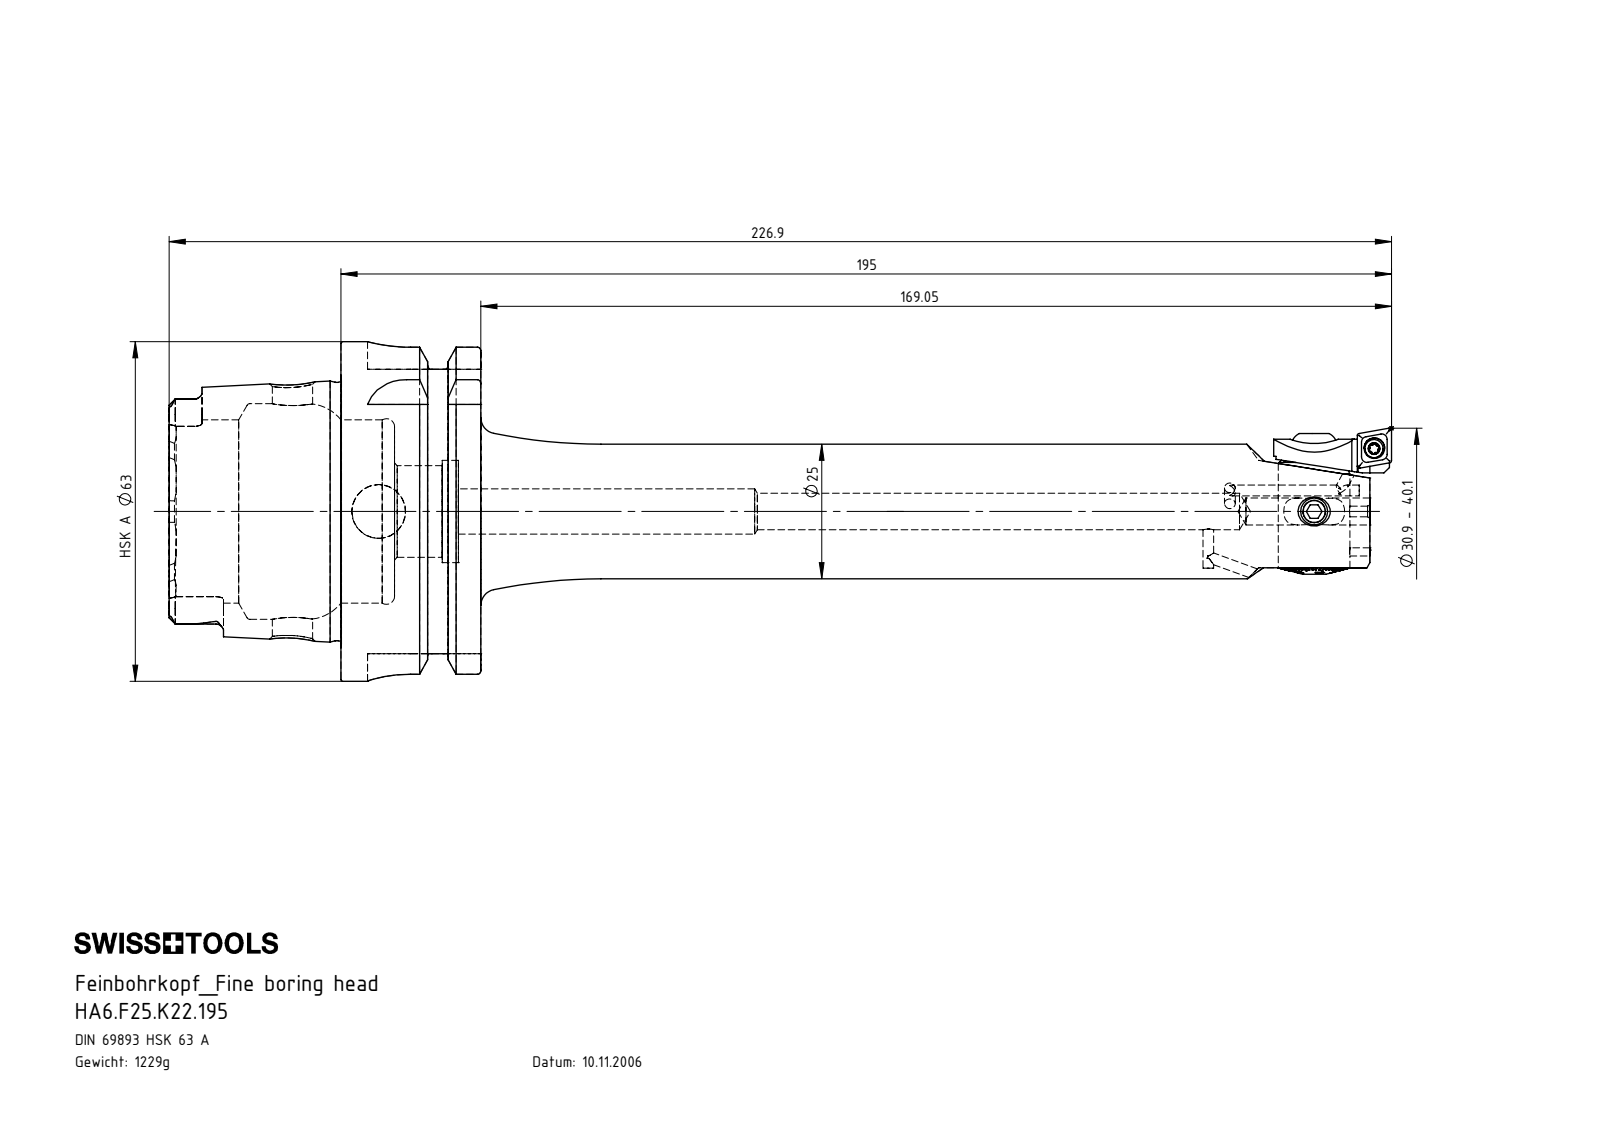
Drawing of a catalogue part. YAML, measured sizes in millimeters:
part_name: "F25-WCA.001.006_D_fertigbearbeitet; F25-BG1.009.006_A; HA6-F25.K20.195_B_Fertigbearbeitung; DIN 3771 - 11x1 (+8 more)"
step_written_by: "SolidWorks 2022 (CONFIG_CONTROL_DESIGN)"
units: millimeters
bodies: {solids: 16, faces: 920, planar: 377, cylindrical: 184, other: 359}
overall_size: [230.25, 63, 63]
volume: 156342
surface_area: 44606
round_holes:
  - {diameter: 2, count: 5}
  - {diameter: 2.05, count: 2}
  - {diameter: 4.2, count: 2}
  - {diameter: 5, count: 2}
  - {diameter: 5.5, count: 2}
  - {diameter: 7.5, count: 2}
  - {diameter: 9, count: 2}
  - {diameter: 10, count: 2}
  - {diameter: 2.1, count: 1}
  - {diameter: 2.4, count: 1}
  - {diameter: 2.7, count: 1}
  - {diameter: 2.8, count: 1}
round_bosses_or_shafts:
  - {diameter: 5, count: 3}
  - {diameter: 13, count: 2}
  - {diameter: 7, count: 2}
  - {diameter: 4.95, count: 2}
  - {diameter: 2.5, count: 2}
  - {diameter: 63, count: 1}
  - {diameter: 54.95, count: 1}
  - {diameter: 47.94, count: 1}
partial_cylinders:
  - {radius: 0.21, count: 6}
  - {radius: 1.4, count: 6}
  - {radius: 0.36, count: 4}
  - {radius: 0.5, count: 4}
  - {radius: 2.88, count: 4}
  - {radius: 8, count: 4}
  - {radius: 0.36, count: 2}
  - {radius: 1.32, count: 2}
face_to_face_distances: [25.95, 16, 9.95, 31.9, 41.85, 57.85, 52.8, 21.8, 11.85, 224.05]
hole_center_spacings: [3.83, 3.99, 4.08, 6.8, 8.9, 18.5, 171.15, 173.65]
